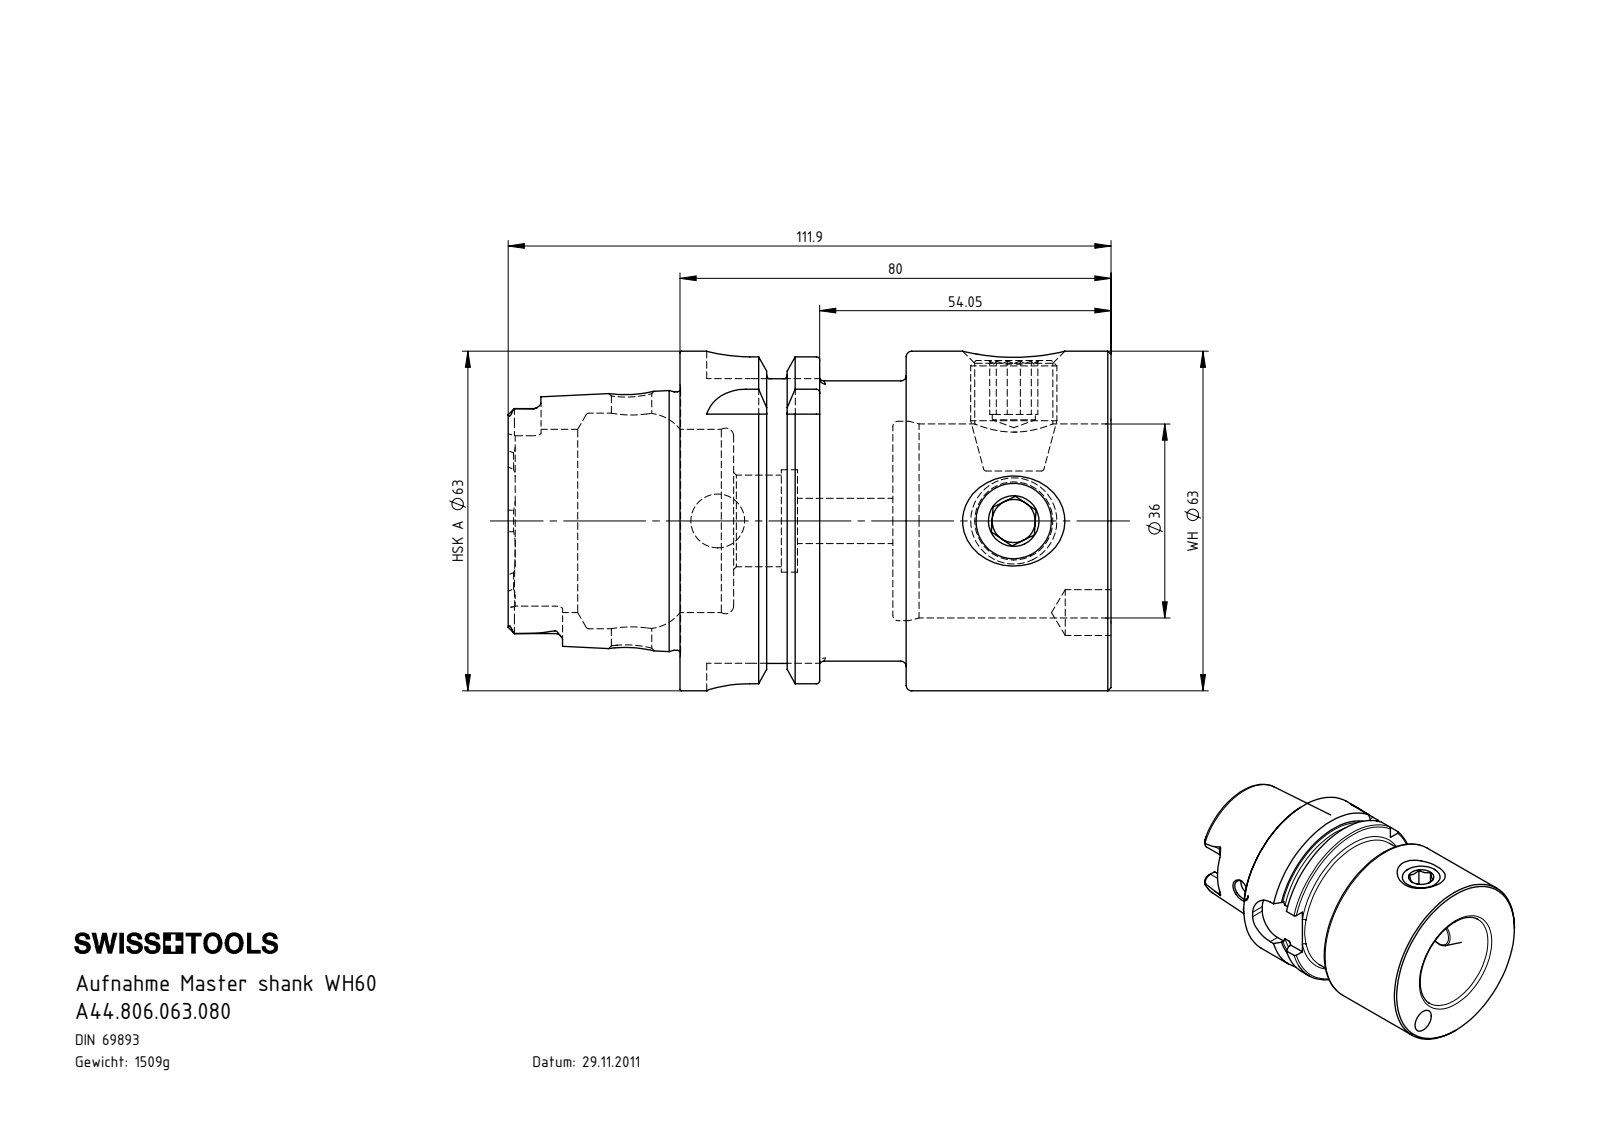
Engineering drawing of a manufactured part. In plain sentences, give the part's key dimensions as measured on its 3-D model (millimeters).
The part is named "A637036". Its 3-D file was written by "SolidWorks 2013 (CONFIG_CONTROL_DESIGN)". It is 1 solid with 26 faces: 8 planar, 12 cylindrical and 6 other. Overall it measures 112 by 63 by 63 millimeters. Its volume is 242 829 cubic millimeters and its surface area 33 697 square millimeters. Round holes: 1 of diameter 36. Round bosses or shafts: 1 of diameter 63, 1 of diameter 55, 1 of diameter 52. The main face-to-face distances are 38, 42, 112, 32, 80, 70, 74, 4, 58, 26.
